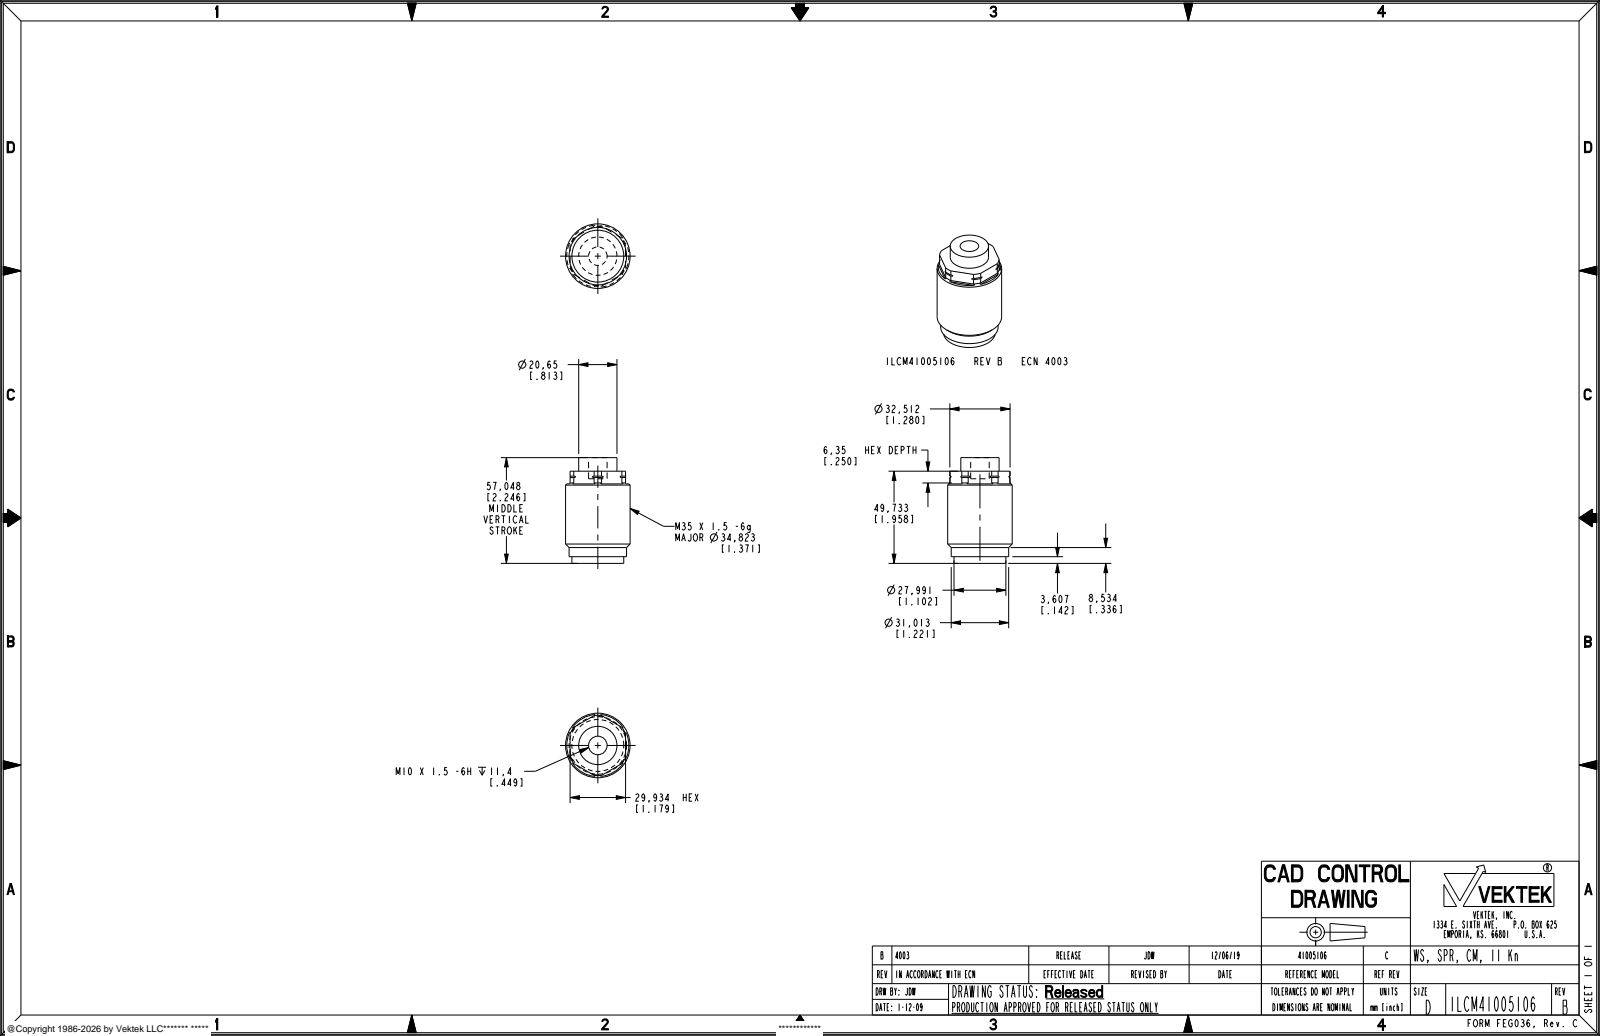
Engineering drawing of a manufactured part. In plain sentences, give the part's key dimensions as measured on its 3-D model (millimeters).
The part is named "ILCM41005106". Its 3-D file was written by "PRO/ENGINEER BY PARAMETRIC TECHNOLOGY CORPORATION, 2013320 (AUTOMOTIVE_DESIGN)". It is 1 solid with 55 faces: 17 planar, 28 cylindrical and 10 other. Overall it measures 57.05 by 34.82 by 34.82 millimeters. Its volume is 45 229 cubic millimeters and its surface area 7 797 square millimeters. Round holes: 1 of diameter 10.01. Round bosses or shafts: 1 of diameter 34.82, 1 of diameter 31.01, 1 of diameter 27.99, 1 of diameter 20.65. Partial cylindrical surfaces (rounded edges, fillets, slot ends): 6 of radius 0.51, 1 of radius 16.26. The main face-to-face distances are 49.73, 57.05, 7.32, 29.94, 3.61, 46.12, 53.44, 45.65, 42.04, 4.08.
